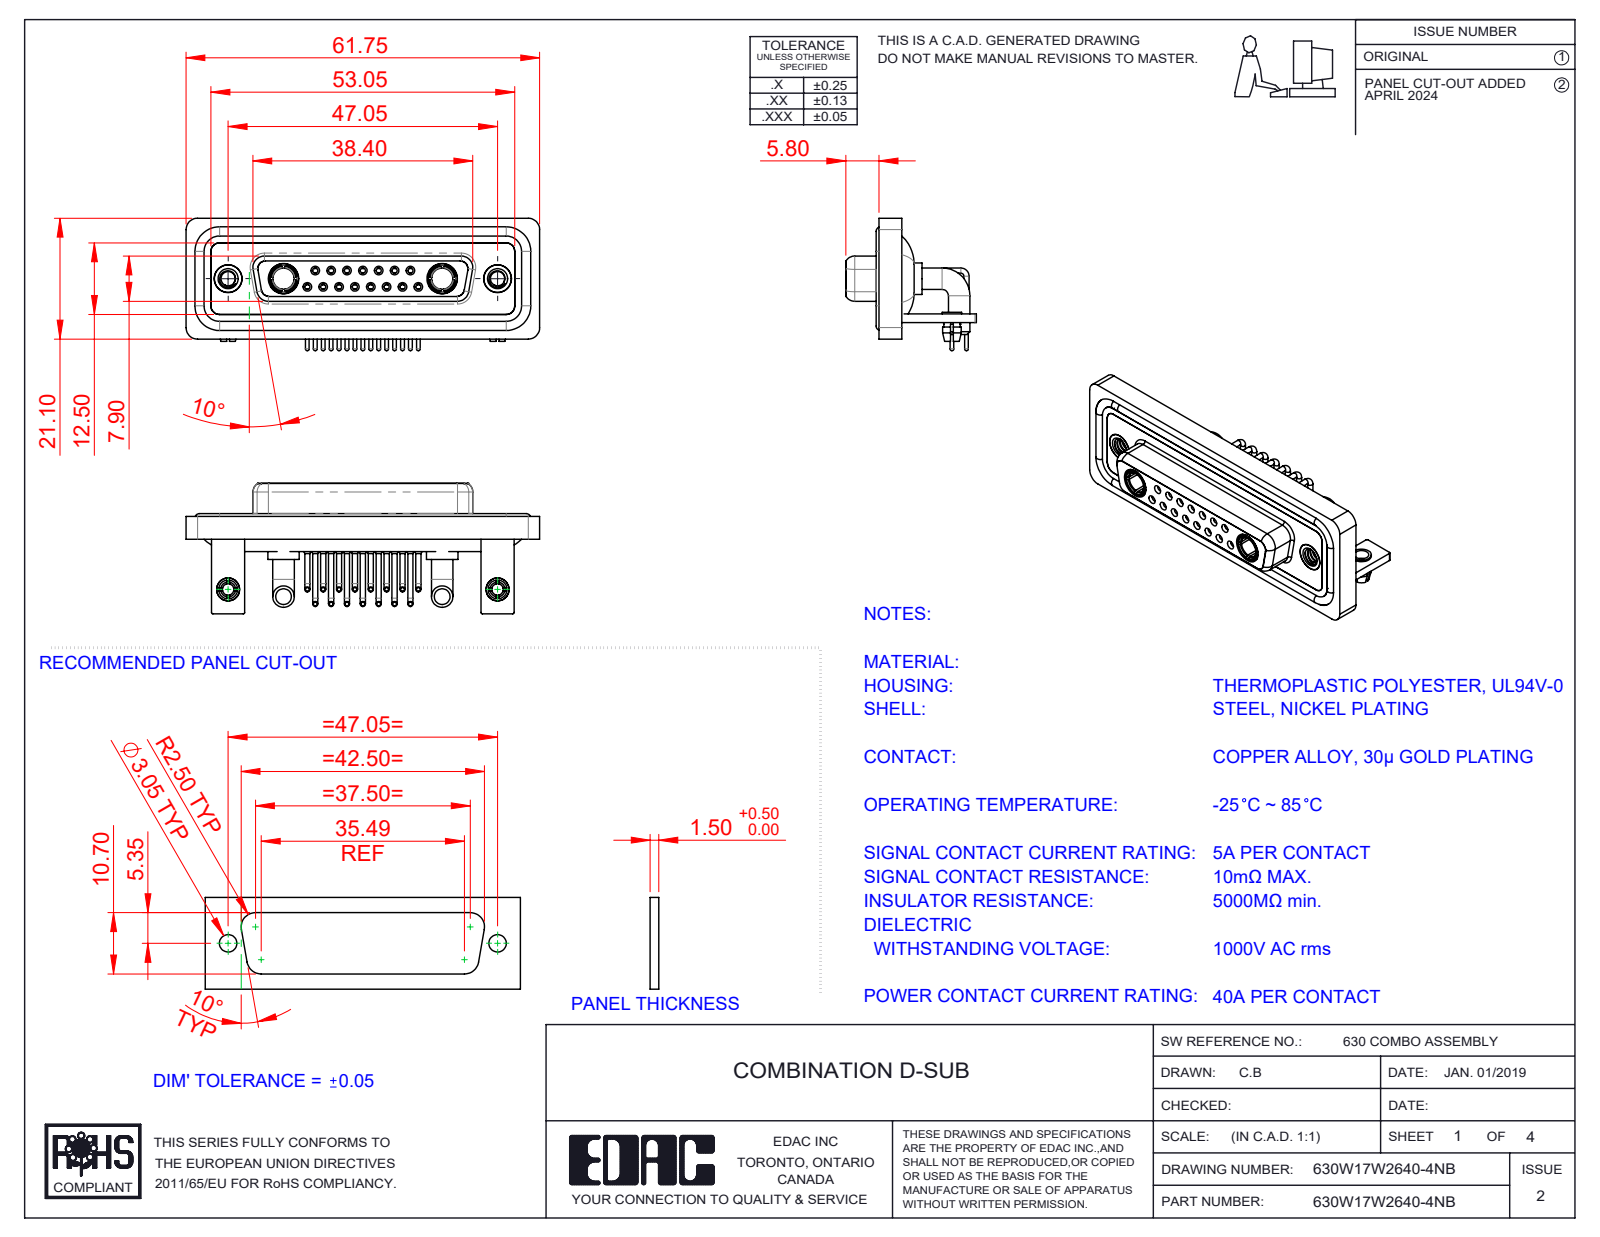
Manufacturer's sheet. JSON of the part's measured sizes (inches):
{"part_name": "630Combo Waterproof Housing_25 Contacts; 630Combo Housing_17W2; 630Combo Threaded Rivet_A; 630Combo Shell Front_25 Contacts (+7 more)", "step_written_by": "SolidWorks 2023 (CONFIG_CONTROL_DESIGN)", "units": "inches", "bodies": {"solids": 30, "faces": 1471, "planar": 456, "cylindrical": 637, "other": 378}, "overall_size": [2.431, 0.91, 0.898], "volume_in3": 0.551, "surface_area_in2": 24.13, "round_holes": [[0.079, 17], [0.035, 15], [0.043, 15], [0.059, 15], [0.063, 8], [0.067, 7], [0.098, 4], [0.191, 4], [0.126, 2], [0.146, 2], [0.157, 2], [0.159, 2]], "round_bosses_or_shafts": [[0.035, 15], [0.026, 15], [0.063, 11], [0.148, 4], [0.217, 2], [0.205, 2], [0.195, 2], [0.195, 2]], "partial_cylinders_radius": [[0.079, 19], [0.059, 18], [0.01, 16], [0.053, 8], [0.063, 8], [0.02, 5], [0.024, 4], [0.026, 4]], "face_to_face_distances": [0.016, 0.071, 0.114, 0.146, 0.059, 0.161, 0.043, 0.055, 0.063, 0.122], "hole_center_spacings": [0.124, 0.109, 0.218, 0.327, 0.198, 0.295, 0.436, 0.198]}
